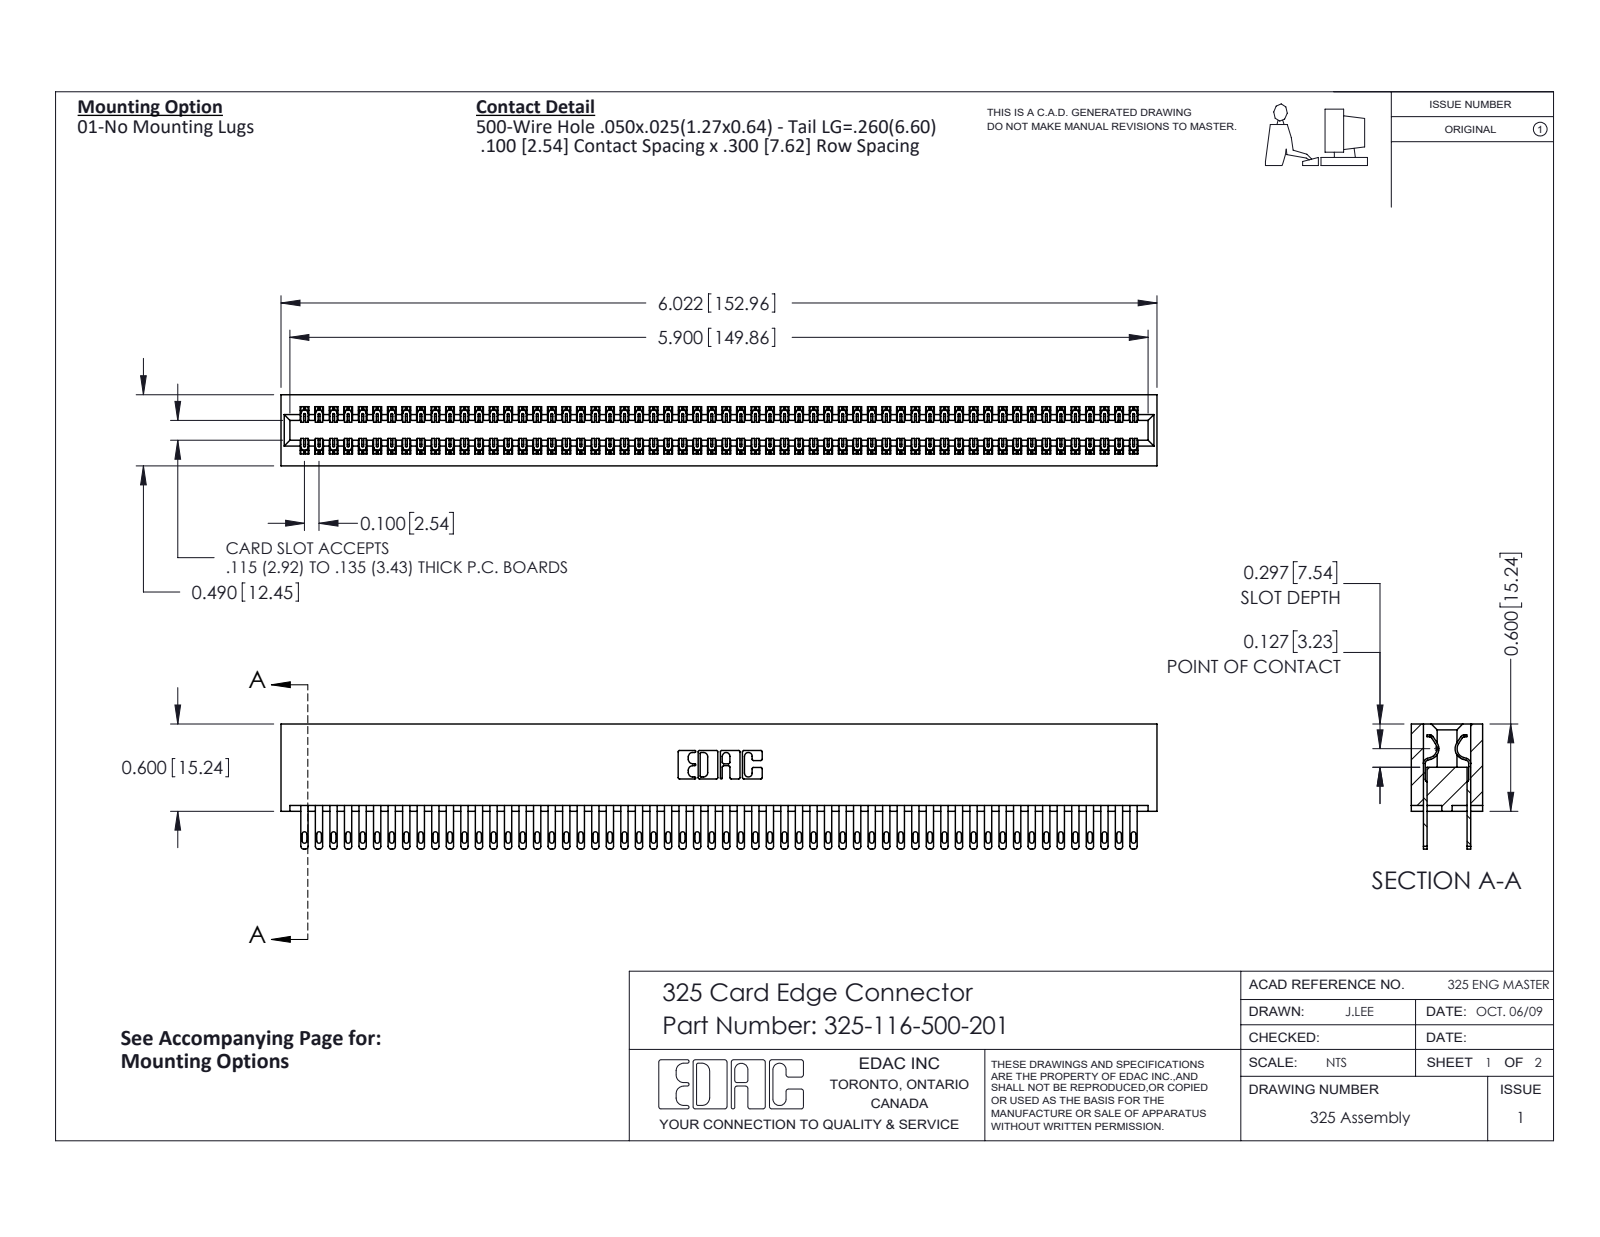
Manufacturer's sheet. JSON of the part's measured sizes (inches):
{"part_name": "325 Part_Lugless; 325-292-001_325-293-100; 325-116-500-201", "step_written_by": "SolidWorks 2016 (CONFIG_CONTROL_DESIGN)", "units": "inches", "bodies": {"solids": 117, "faces": 5674, "planar": 3546, "cylindrical": 2128, "other": 0}, "overall_size": [6.022, 0.86, 0.49], "volume_in3": 1.272, "surface_area_in2": 42.61, "partial_cylinders_radius": [[0.006, 174], [0.016, 116], [0.02, 116], [0.01, 22], [0.007, 6], [0.031, 6], [0.026, 3], [0.014, 2]], "face_to_face_distances": [0.083, 0.407, 0.3, 0.107, 0.383, 0.025, 0.325, 0.49, 0.275, 0.263]}
